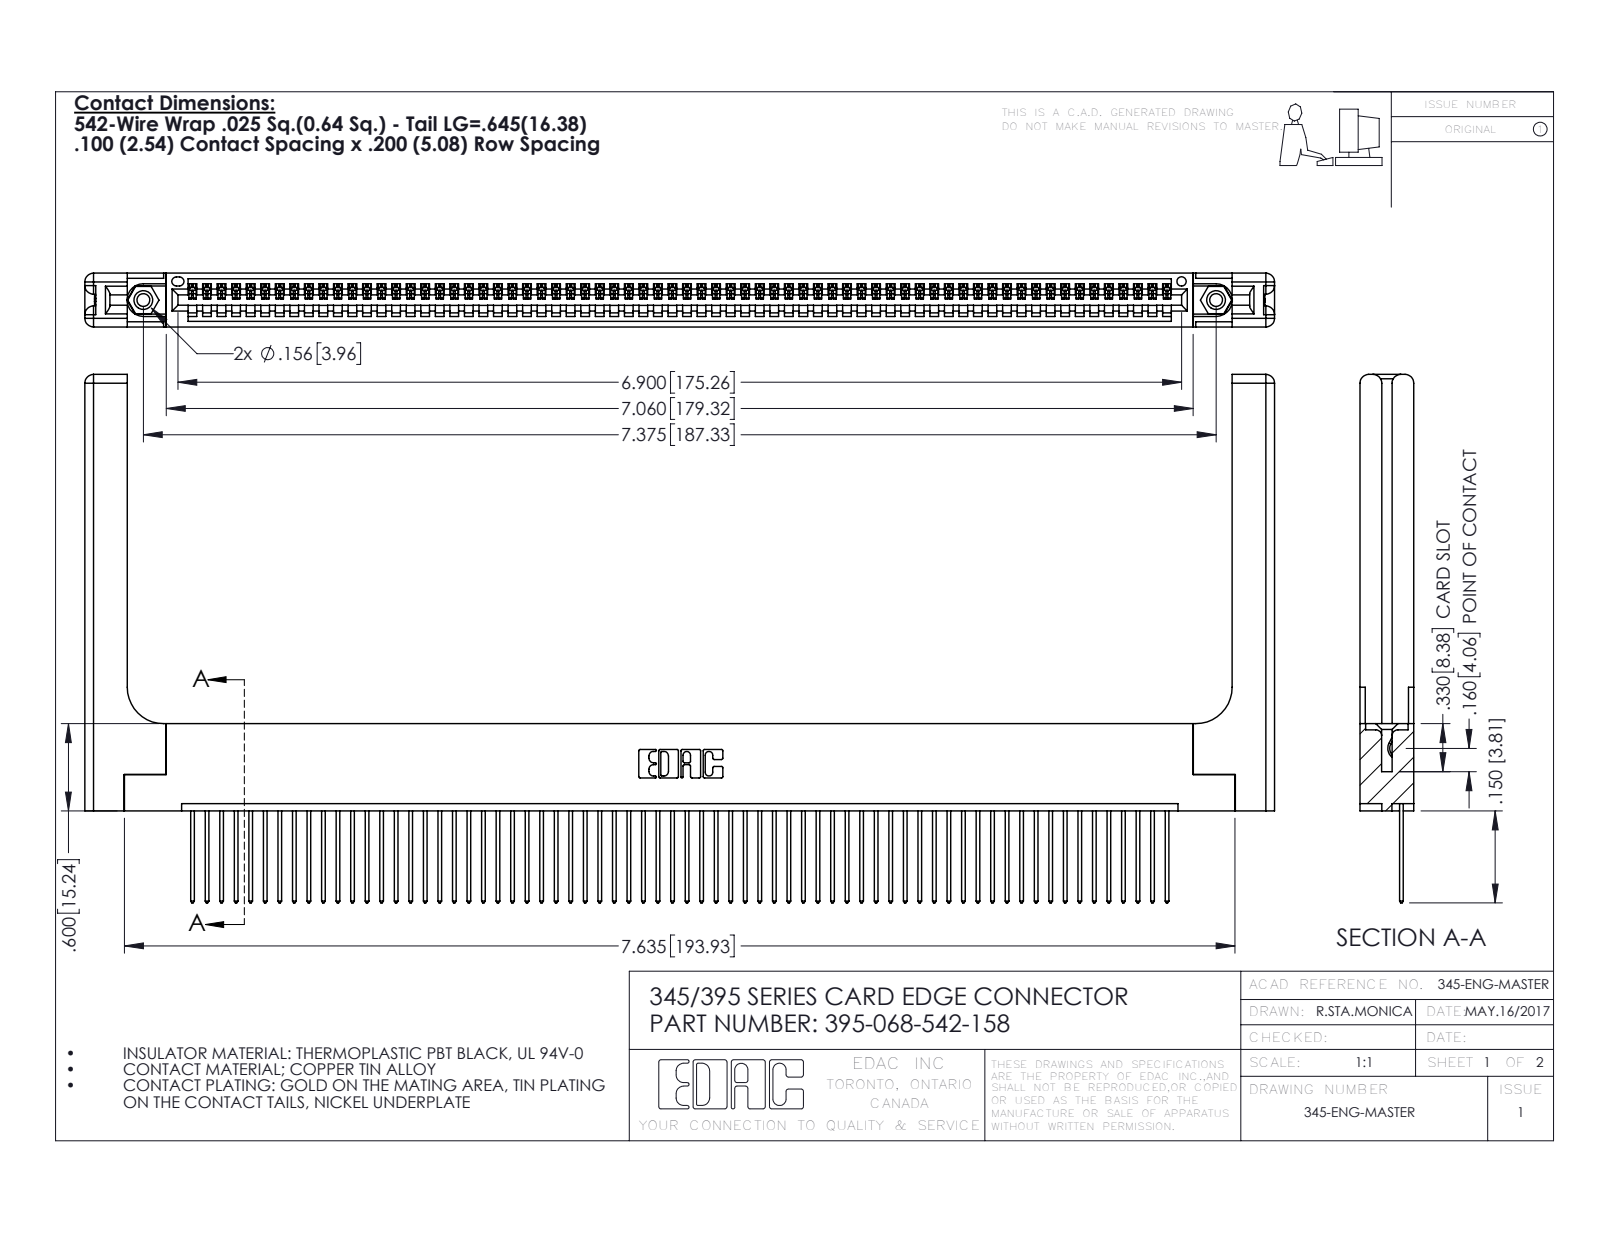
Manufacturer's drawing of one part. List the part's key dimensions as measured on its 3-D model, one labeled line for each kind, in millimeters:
Part name (STEP PRODUCT): 395-068-542-158; 345 Part_Flush Mounting Lugs - 0.156 Dia-TH; 345-220-058_345-220-058; 345-250-001_345-250-001-102 (+1 more)
STEP written by: SolidWorks 2016 (CONFIG_CONTROL_DESIGN)
Units: millimetres
Bodies: 73 solids, 4326 faces (2948 planar, 1318 cylindrical, 60 other)
Overall size (bounding box): 207.7 × 92.3 × 9.4
Volume: 28 600 mm³ · Surface area: 33 320 mm²
Round holes (diameter × count): ⌀2.3 ×2, ⌀3.2 ×2, ⌀4 ×2, ⌀1.6 ×1
Round bosses / shafts (diameter × count): ⌀3.9 ×2
Partial cylindrical surfaces — rounded edges, fillets, slot ends (radius × count): R0.2 ×136, R0.3 ×136, R0.3 ×22, R1.5 ×16, R0.2 ×6, R0.8 ×6, R0.7 ×3, R0.8 ×2
Main face-to-face distances: 1.8, 7.6, 9.4, 2.5, 6.9, 0.6, 5.1, 5.7, 3.8, 3.8
Hole centre spacings: 6.9, 181.3, 187.3
